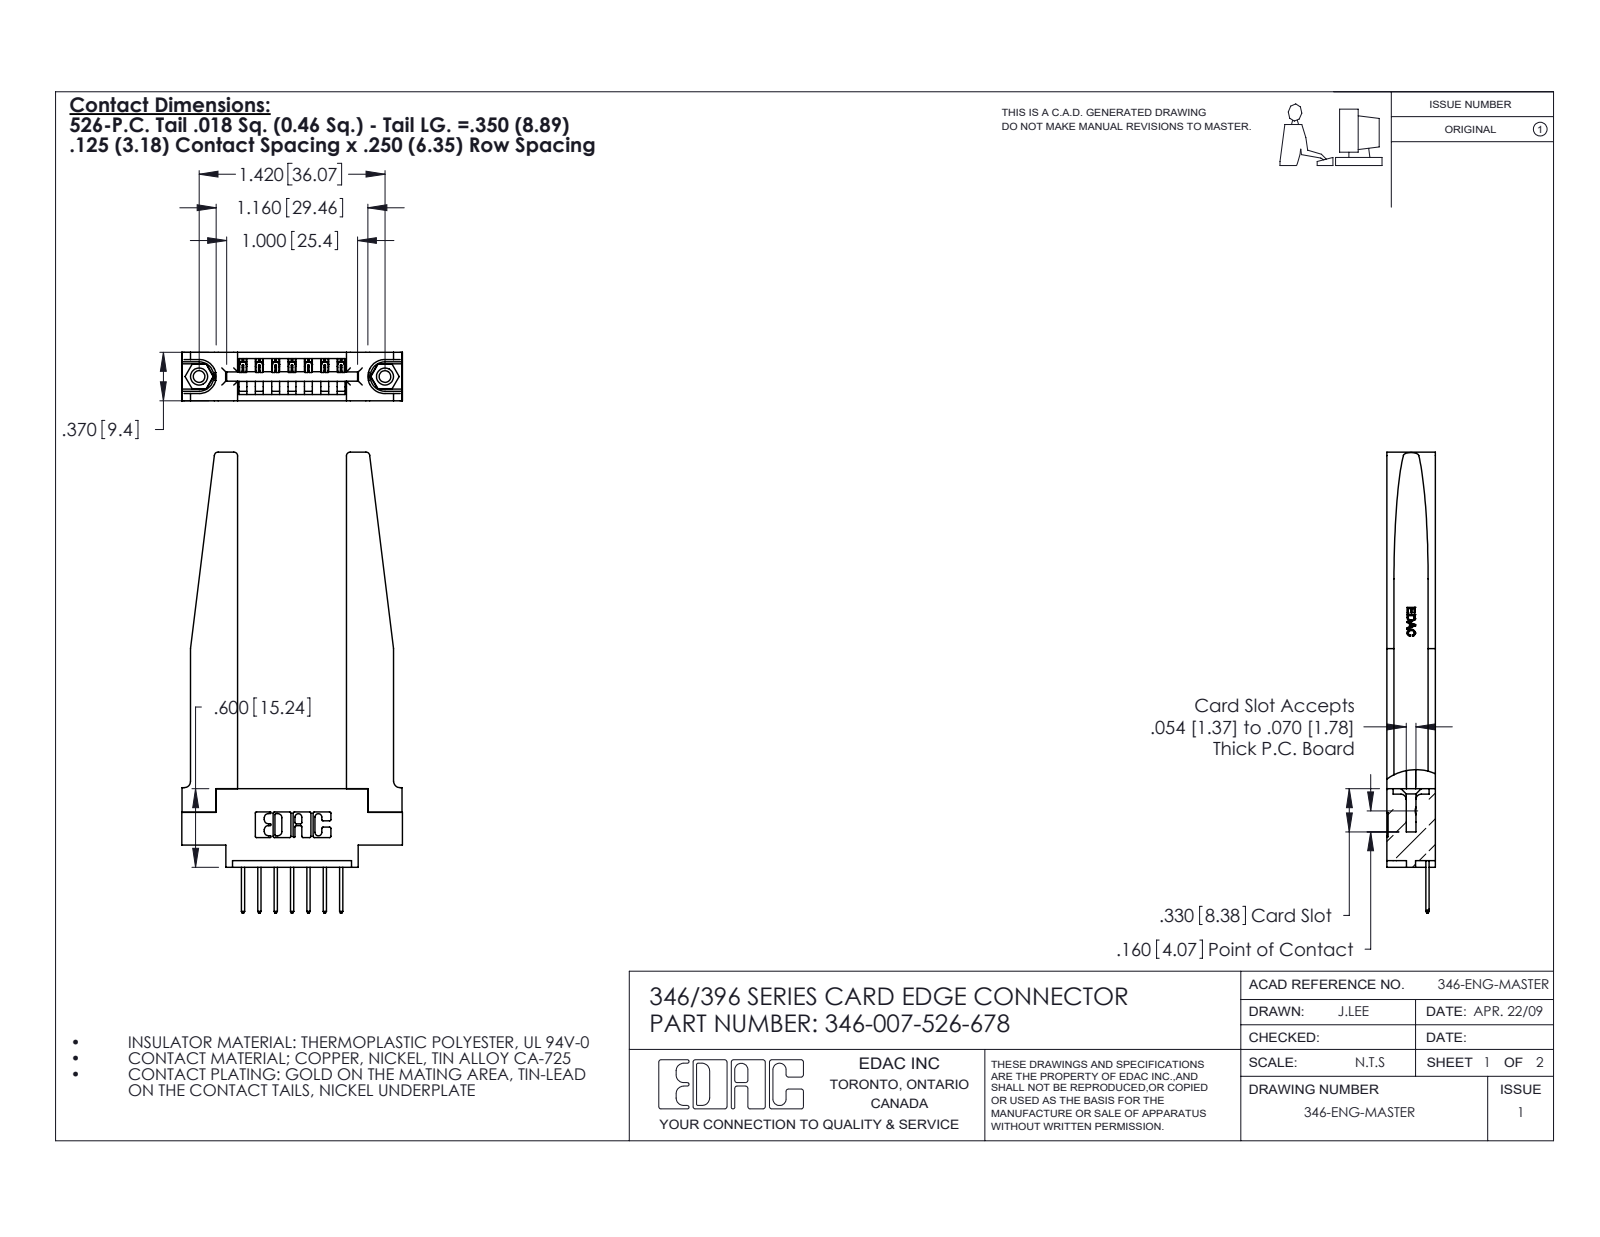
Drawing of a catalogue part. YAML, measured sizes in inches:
part_name: "346 Part_0.170 Offset - 0.156 Dia-TH; 345-292-001_345-293-126; 345-250-001_345-250-001-102; 346-007-526-678 (+1 more)"
step_written_by: "SolidWorks 2020 (CONFIG_CONTROL_DESIGN)"
units: inches
bodies: {solids: 12, faces: 780, planar: 516, cylindrical: 212, other: 52}
overall_size: [3.52, 1.685, 0.37]
volume: 0.646
surface_area: 16.96
round_holes:
  - {diameter: 0.089, count: 2}
  - {diameter: 0.125, count: 2}
  - {diameter: 0.156, count: 2}
  - {diameter: 0.064, count: 1}
round_bosses_or_shafts:
  - {diameter: 0.155, count: 2}
partial_cylinders:
  - {radius: 0.01, count: 22}
  - {radius: 0.006, count: 14}
  - {radius: 0.01, count: 14}
  - {radius: 0.03, count: 8}
  - {radius: 0.007, count: 6}
  - {radius: 0.031, count: 6}
  - {radius: 0.026, count: 3}
  - {radius: 0.031, count: 2}
face_to_face_distances: [0.37, 0.15, 0.22, 0.25, 0.072, 0.148, 0.831, 0.048, 0.322, 0.102]
hole_center_spacings: [0.246, 1.217, 1.42]
